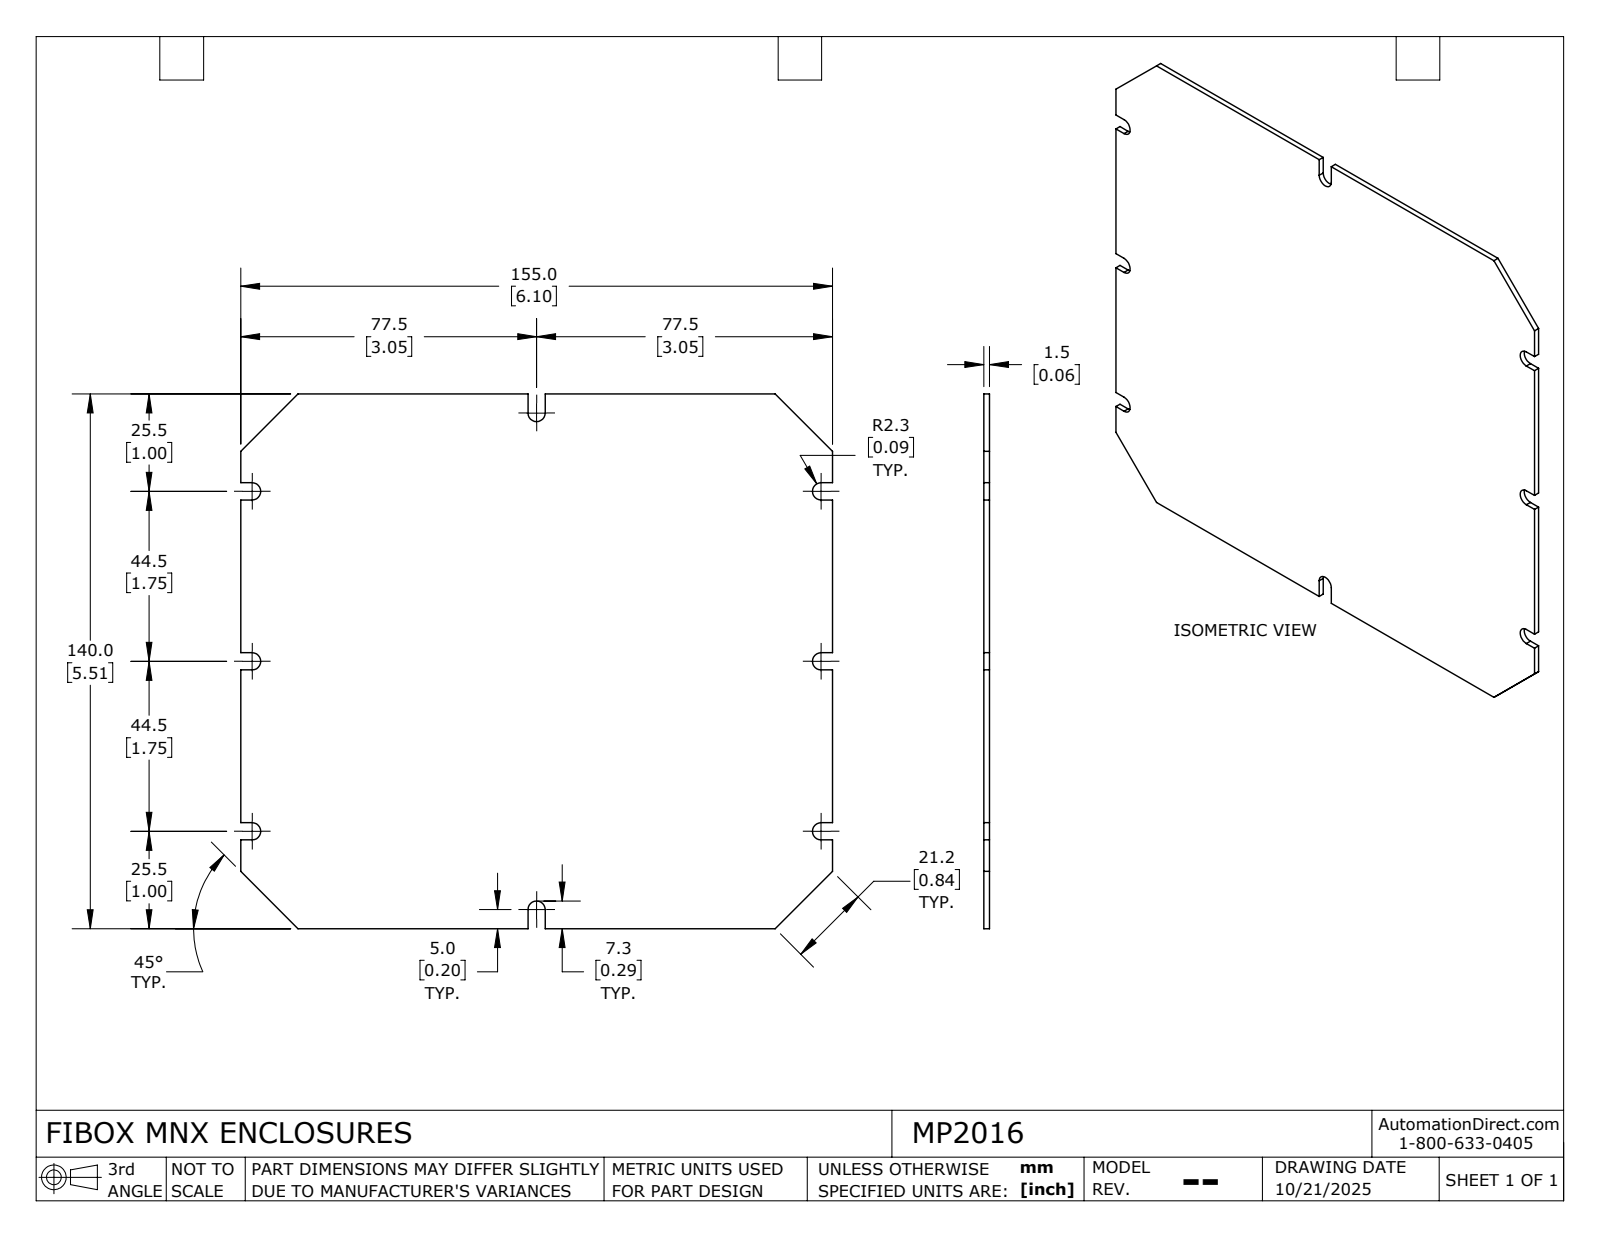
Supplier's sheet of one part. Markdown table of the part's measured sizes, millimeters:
| quantity | value |
| --- | --- |
| part name | MP2016_Default |
| STEP written by | SolidWorks 2024 (CONFIG_CONTROL_DESIGN) |
| units | millimeters |
| bodies | 1 solid, 42 faces (34 planar, 8 cylindrical, 0 other) |
| overall size | 155 × 140 × 1.5 |
| volume | 31 591 mm³ |
| surface area | 43 068 mm² |
| partial cylindrical surfaces (radius × count) | 2.25 × 8 |
| main face-to-face distances | 1.5, 140, 155, 187.36, 4.5, 44.5, 75.25, 79.75, 23.25, 27.75 |
